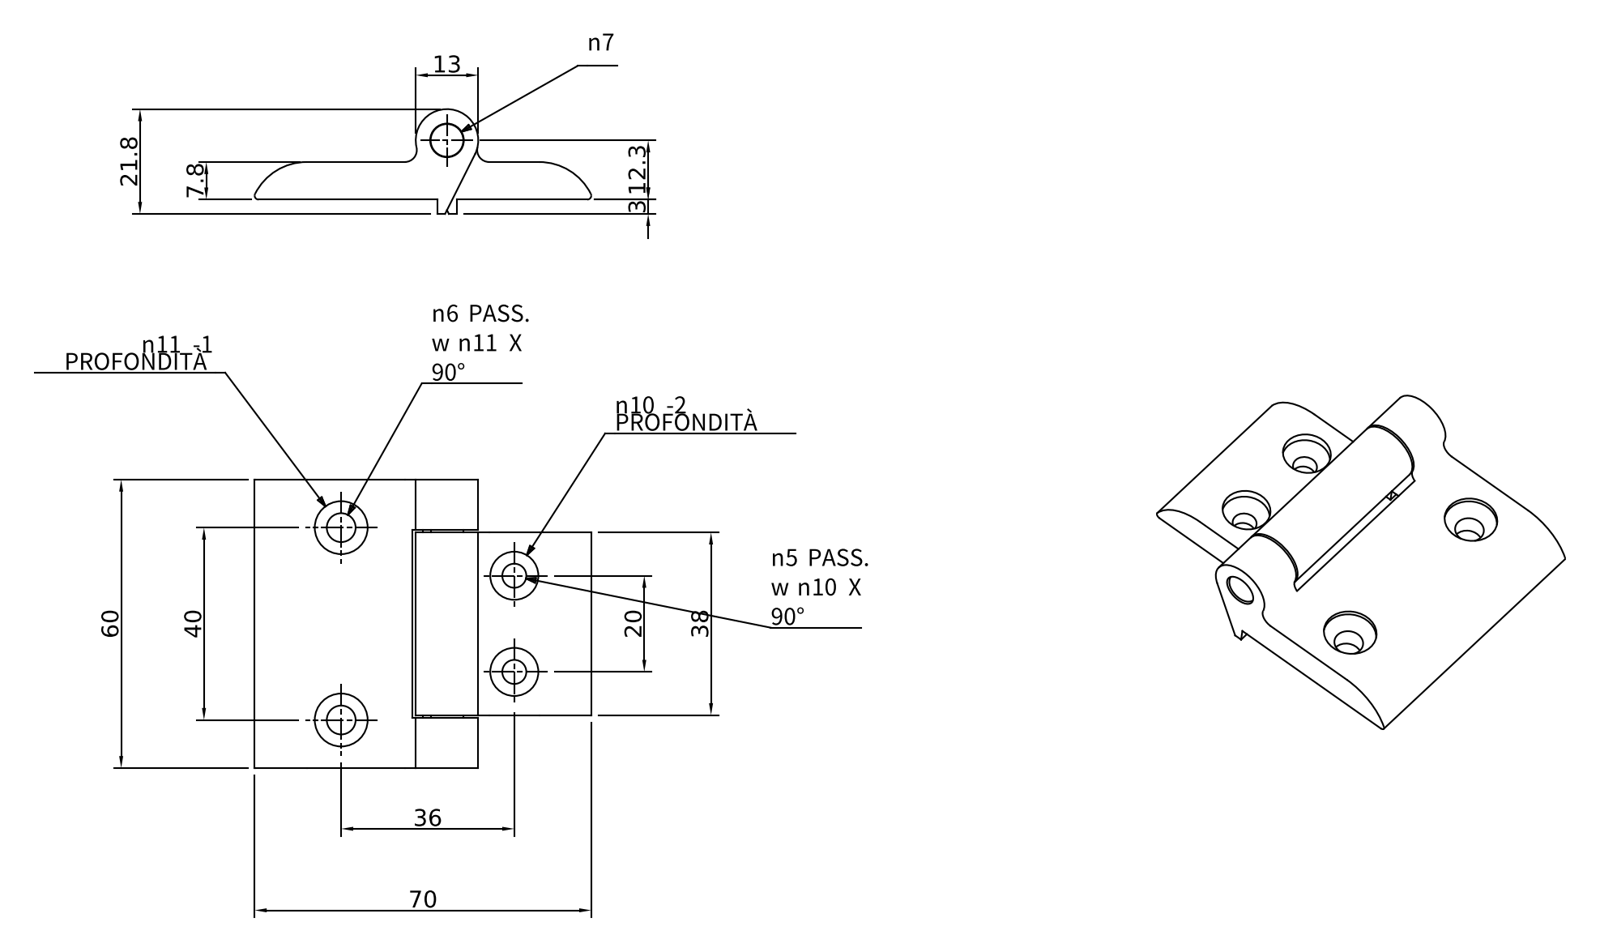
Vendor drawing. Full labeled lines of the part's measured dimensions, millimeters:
Part name (STEP PRODUCT): CCRYY0000015; 440000010433; 440000010434; 958510007799
STEP written by: Autodesk Inventor 2019 (AUTOMOTIVE_DESIGN)
Units: millimetres
Bodies: 3 solids, 49 faces (22 planar, 19 cylindrical, 8 other)
Overall size (bounding box): 70 × 60 × 21.8
Volume: 31 317 mm³ · Surface area: 14 255 mm²
Round holes (diameter × count): ⌀5 ×2, ⌀6 ×2, ⌀10 ×2, ⌀11 ×2, ⌀7 ×1
Round bosses / shafts (diameter × count): ⌀6.8 ×1
Partial cylindrical surfaces — rounded edges, fillets, slot ends (radius × count): R2.5 ×2, R12 ×2, R6.5 ×1
Main face-to-face distances: 7.8, 11, 49, 60, 38, 10.5, 49.5, 0.5, 38.5, 39
Hole centre spacings: 37.36, 46.86, 20, 40
